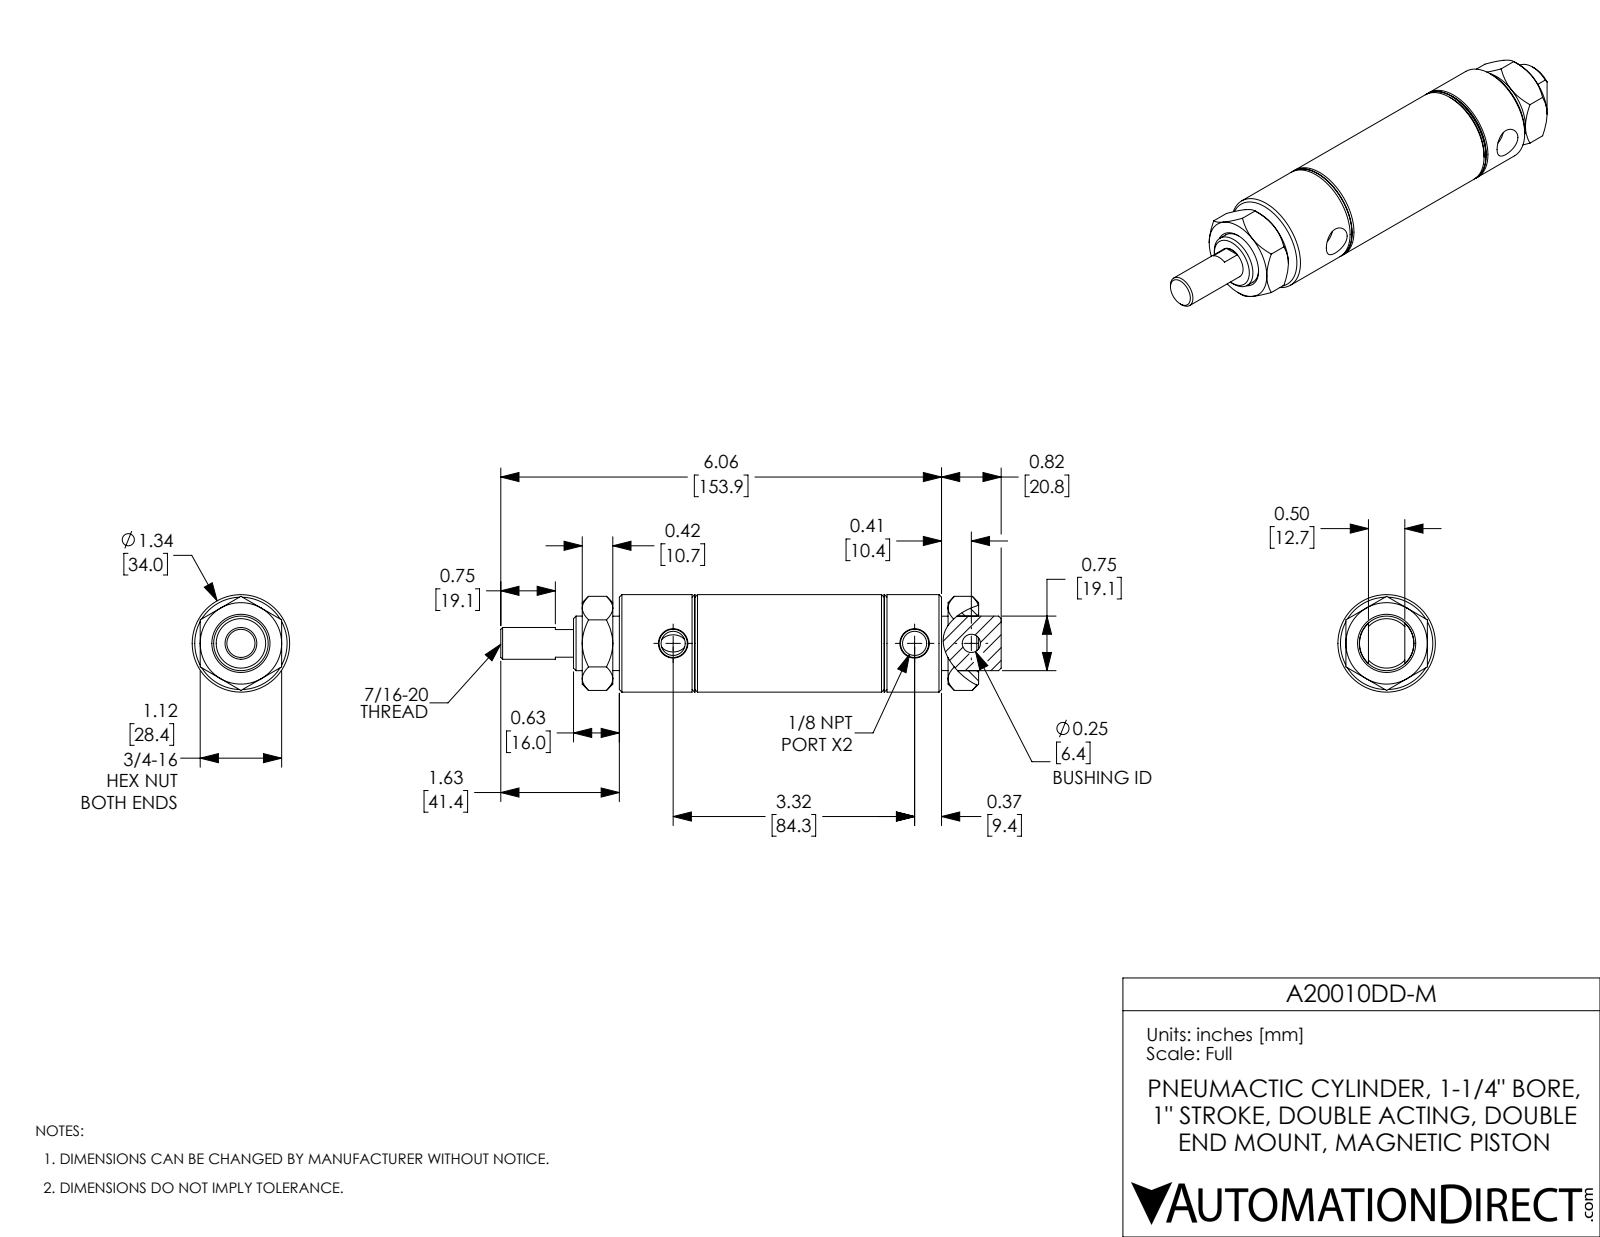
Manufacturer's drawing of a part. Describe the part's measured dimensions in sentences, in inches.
The part is named "A20010DD-M-Rod; A20010DD-M-MainBody; A20010DD-M; A20010DD-M_Mounting Nut_D-3556". Its 3-D file was written by "SolidWorks 2017 (AUTOMOTIVE_DESIGN)". It is 4 solids with 138 faces: 44 planar, 36 cylindrical and 58 other. Overall it measures 6.88 by 1.34 by 1.34 inches. Its volume is 6.272 cubic inches and its surface area 54.86 square inches. Round holes: 2 of diameter 0.332, 1 of diameter 0.251, 1 of diameter 0.437, 1 of diameter 0.75, 1 of diameter 1.25. Round bosses or shafts: 1 of diameter 1.34, 1 of diameter 0.747. The main face-to-face distances are 1.465, 2.965, 0.5, 1.12, 1, 1.5, 0.31, 1.965, 0.42, 5.03. The hole center spacings are 0.78, 3.32, 4.1.
